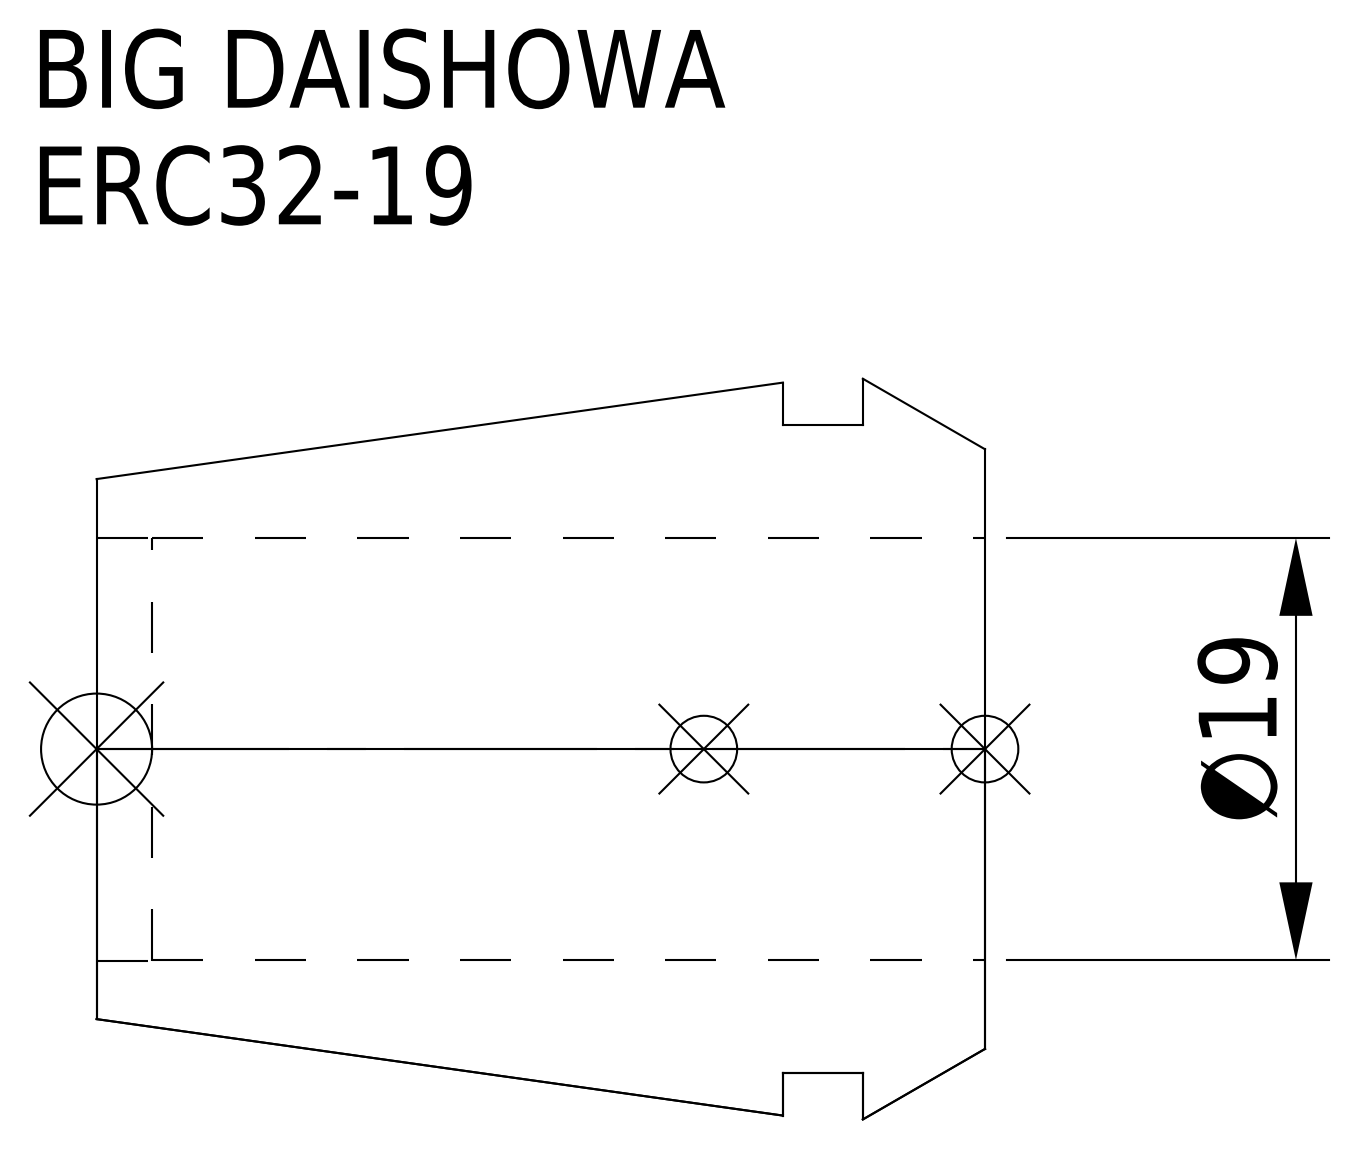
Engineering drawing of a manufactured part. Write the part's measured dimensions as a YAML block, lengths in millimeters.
part_name: "ERC32-19"
step_written_by: "CREO PARAMETRIC BY PTC INC, 2016380 (AUTOMOTIVE_DESIGN)"
units: millimeters
bodies: {solids: 1, faces: 15, planar: 5, cylindrical: 6, other: 4}
overall_size: [40, 33.35, 33.35]
volume: 15098
surface_area: 6989
round_holes:
  - {diameter: 19, count: 1}
  - {diameter: 19.05, count: 1}
round_bosses_or_shafts:
  - {diameter: 29.2, count: 1}
face_to_face_distances: [5.5, 9.1, 3.6, 40, 34.5, 30.9, 37.5, 32, 28.4, 2.5]
